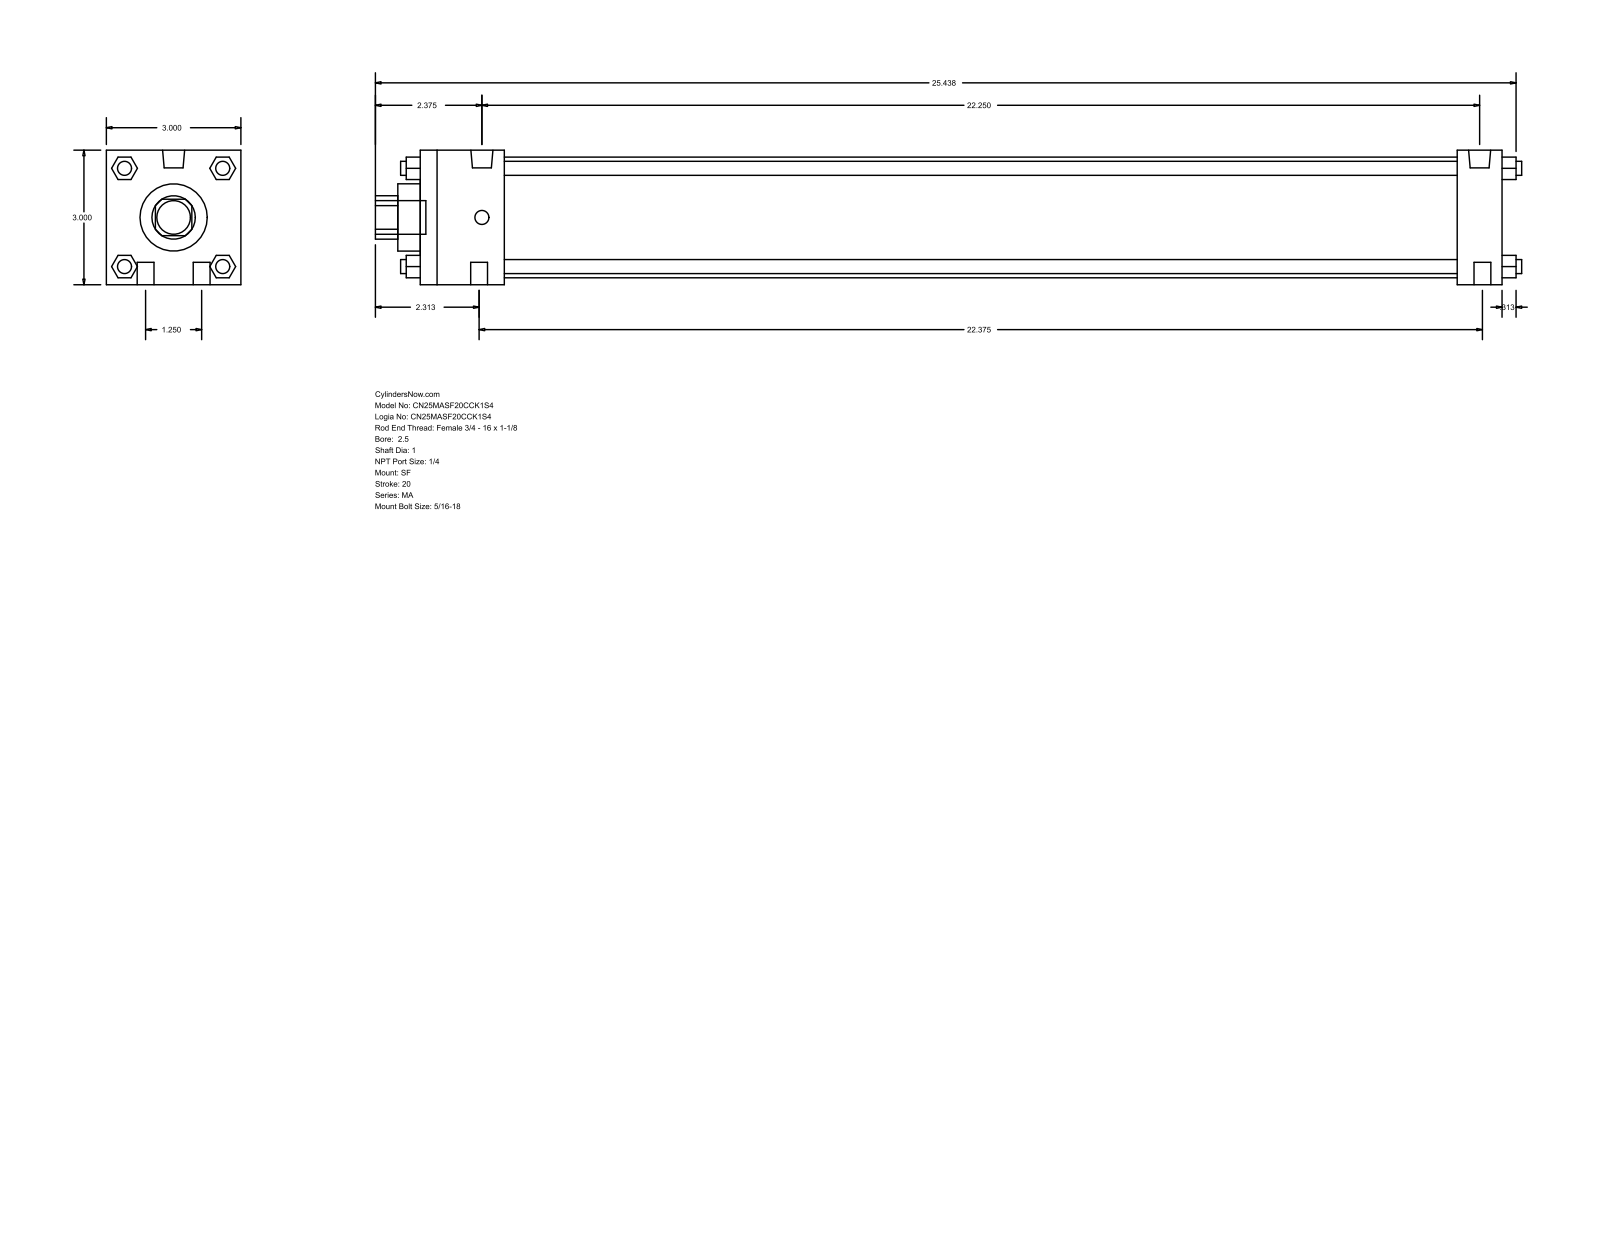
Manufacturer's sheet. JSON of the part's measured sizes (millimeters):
{"part_name": "MA_SF__0250_1", "step_written_by": "GSSL Pune (CONFIG_CONTROL_DESIGN)", "units": "millimeters", "bodies": {"solids": 0, "faces": 124, "planar": 94, "cylindrical": 30, "other": 0}, "overall_size": [649.29, 76.2, 76.2], "round_holes": [[25.4, 1], [38.1, 1], [68.33, 1]], "round_bosses_or_shafts": [[7.94, 6], [9.53, 4], [12.49, 2], [19.05, 1]], "partial_cylinders_radius": [[12.29, 1]], "face_to_face_distances": [76.2, 612.77, 12.7, 25.4, 587.37, 47.63, 539.74, 565.14, 27.81, 48.17]}
